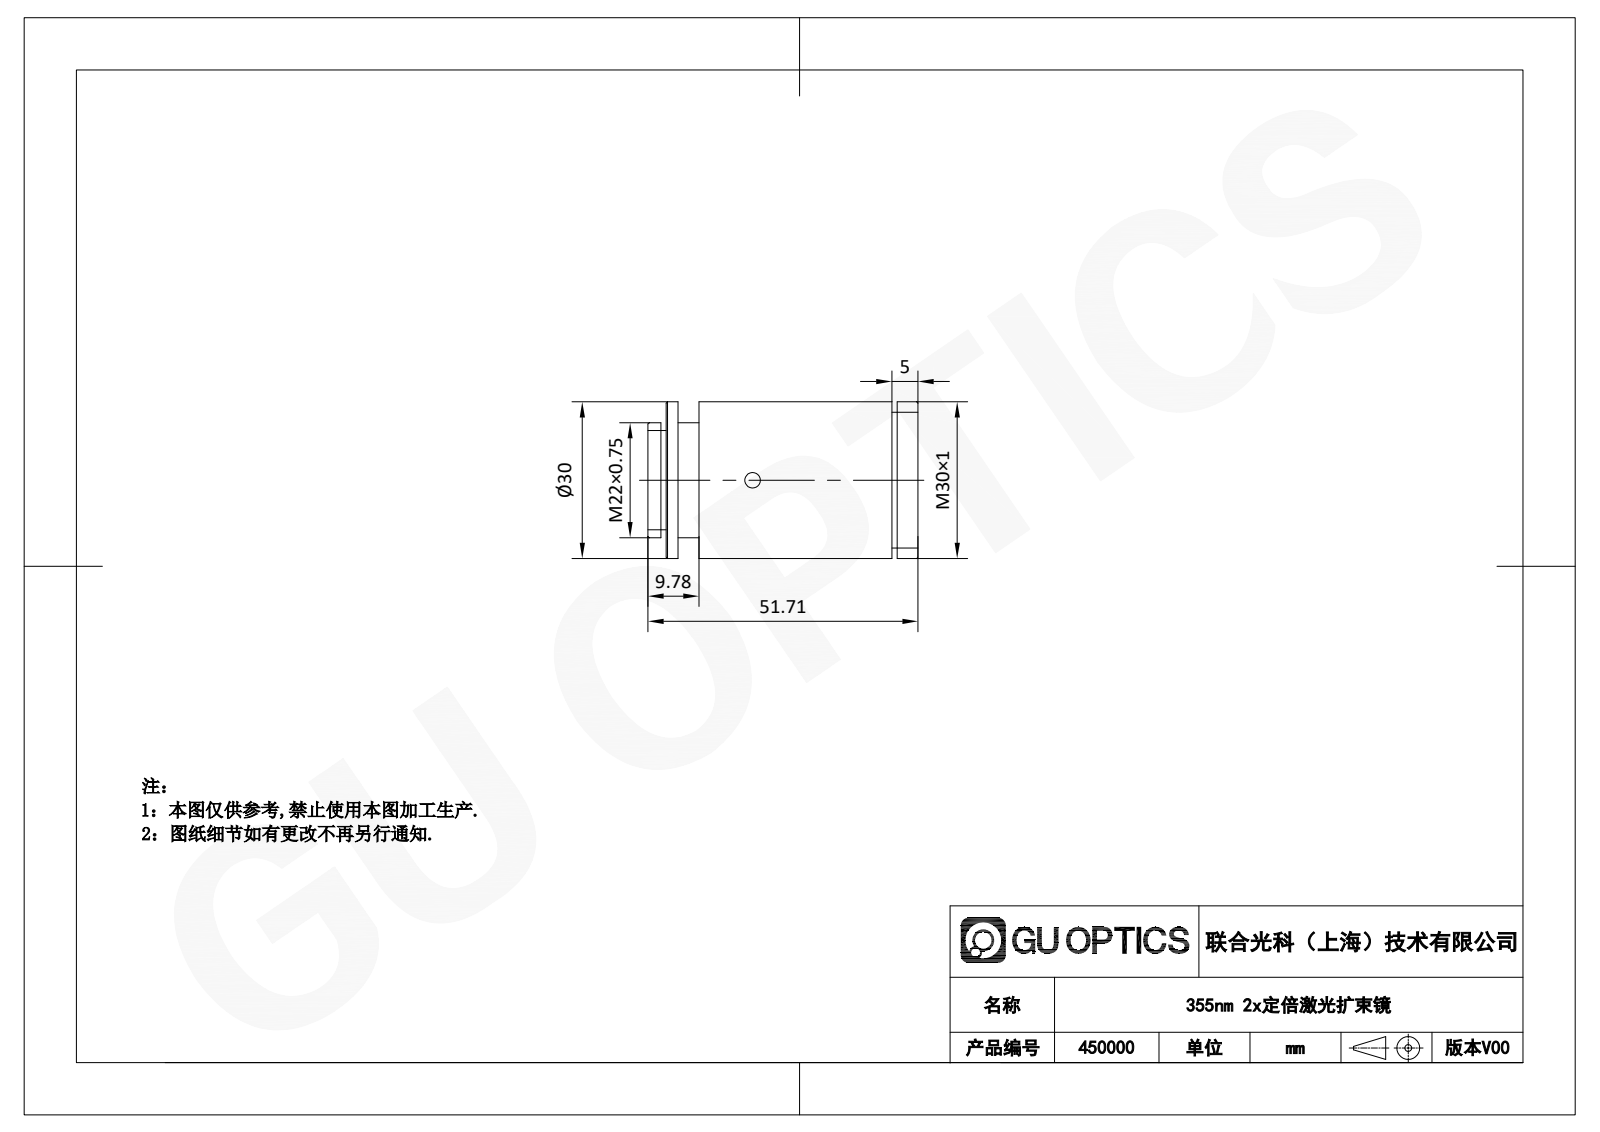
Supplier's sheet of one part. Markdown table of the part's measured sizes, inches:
| quantity | value |
| --- | --- |
| part name | 450000 |
| STEP written by | SolidWorks 2020 (AUTOMOTIVE_DESIGN) |
| units | inches |
| bodies | 1 solid, 51 faces (11 planar, 22 cylindrical, 18 other) |
| overall size | 2.036 × 1.181 × 1.181 |
| volume | 1.633 in³ |
| surface area | 15.02 in² |
| round holes (diameter × count) | 0.315 × 1, 0.709 × 1 |
| round bosses / shafts (diameter × count) | 1.181 × 1, 1.024 × 1, 0.866 × 1, 0.748 × 1 |
| main face-to-face distances | 0.157, 1.651, 0.039, 1.898, 1.78, 0.138, 2.036, 0.228, 0.09, 1.808 |
